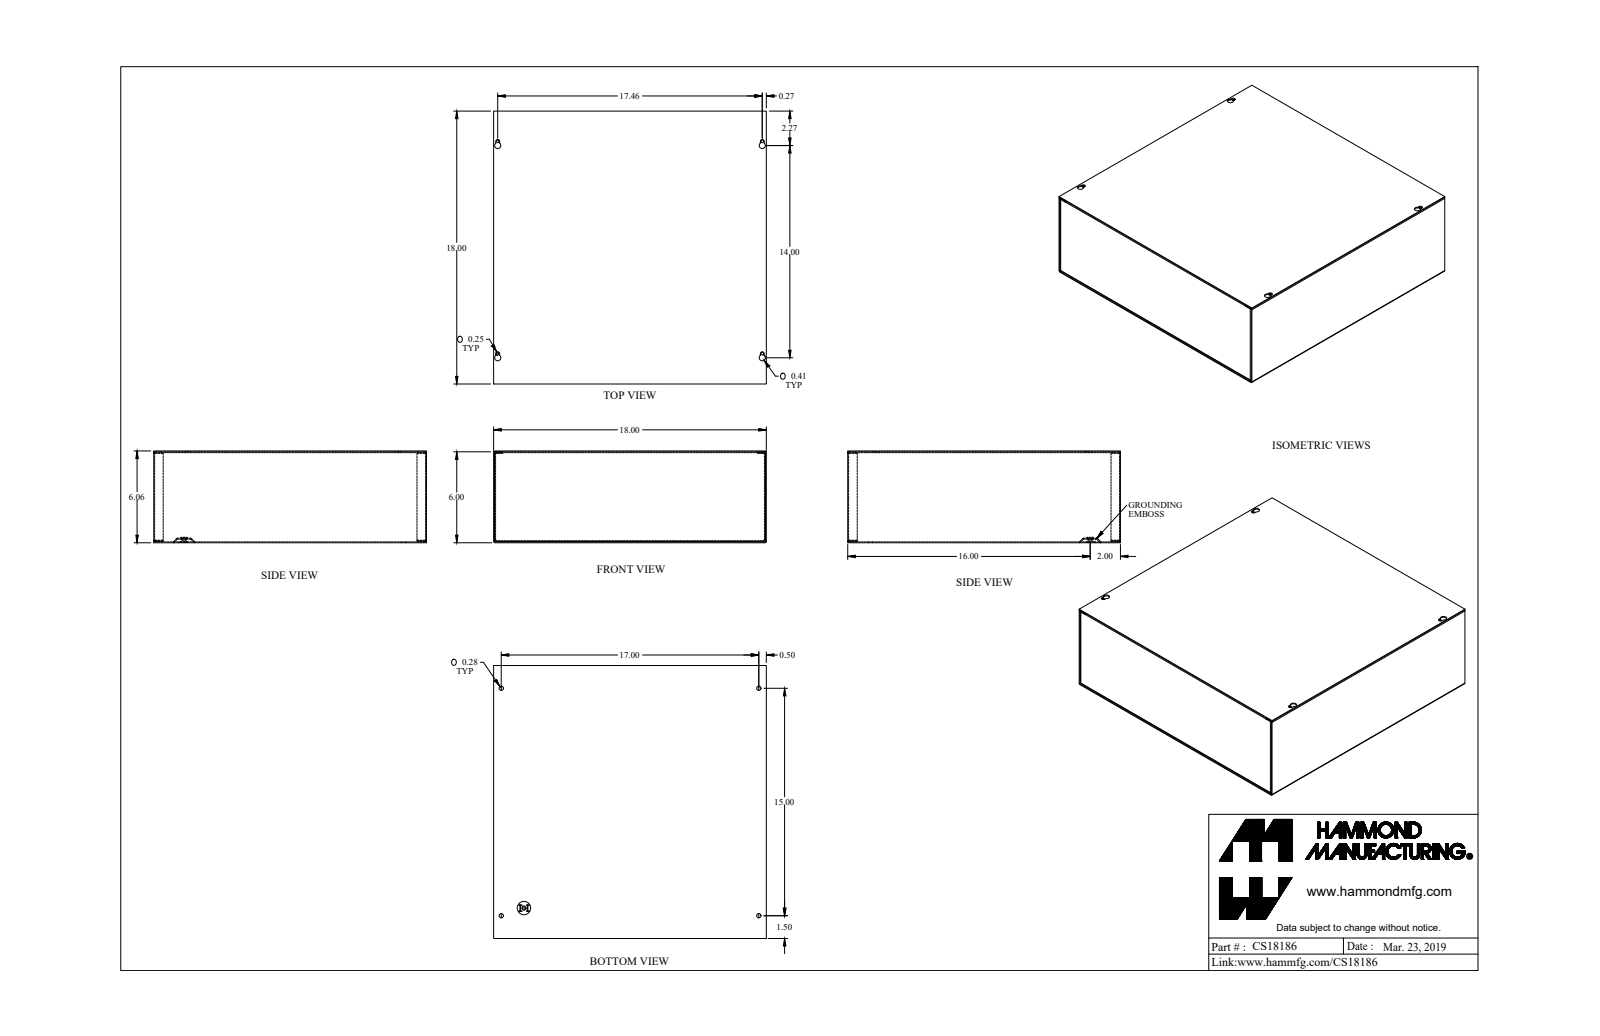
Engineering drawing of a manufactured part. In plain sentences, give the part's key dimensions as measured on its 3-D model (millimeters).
The part is named "CS18186_Default". Its 3-D file was written by "SolidWorks 2019 (CONFIG_CONTROL_DESIGN)". It is 4 solids with 205 faces: 125 planar, 72 cylindrical and 8 other. Overall it measures 457.2 by 457.2 by 153.8 millimeters. Its volume is 1 058 000 cubic millimeters and its surface area 1 472 000 square millimeters. Round holes: 5 of diameter 4.3, 4 of diameter 7.1, 1 of diameter 12.7. Round bosses or shafts: 1 of diameter 12.5, 1 of diameter 7.2. Partial cylindrical surfaces (rounded edges, fillets, slot ends): 12 of radius 0.7, 12 of radius 2.2, 8 of radius 1.4, 4 of radius 3.2, 4 of radius 5.2. The main face-to-face distances are 1.4, 152.4, 455.8, 151, 153.8, 457.2, 454.3, 2, 148.9, 150.4. The hole center spacings are 14, 368.4, 437.8, 572, 355.6, 381, 431.8, 443.5.
